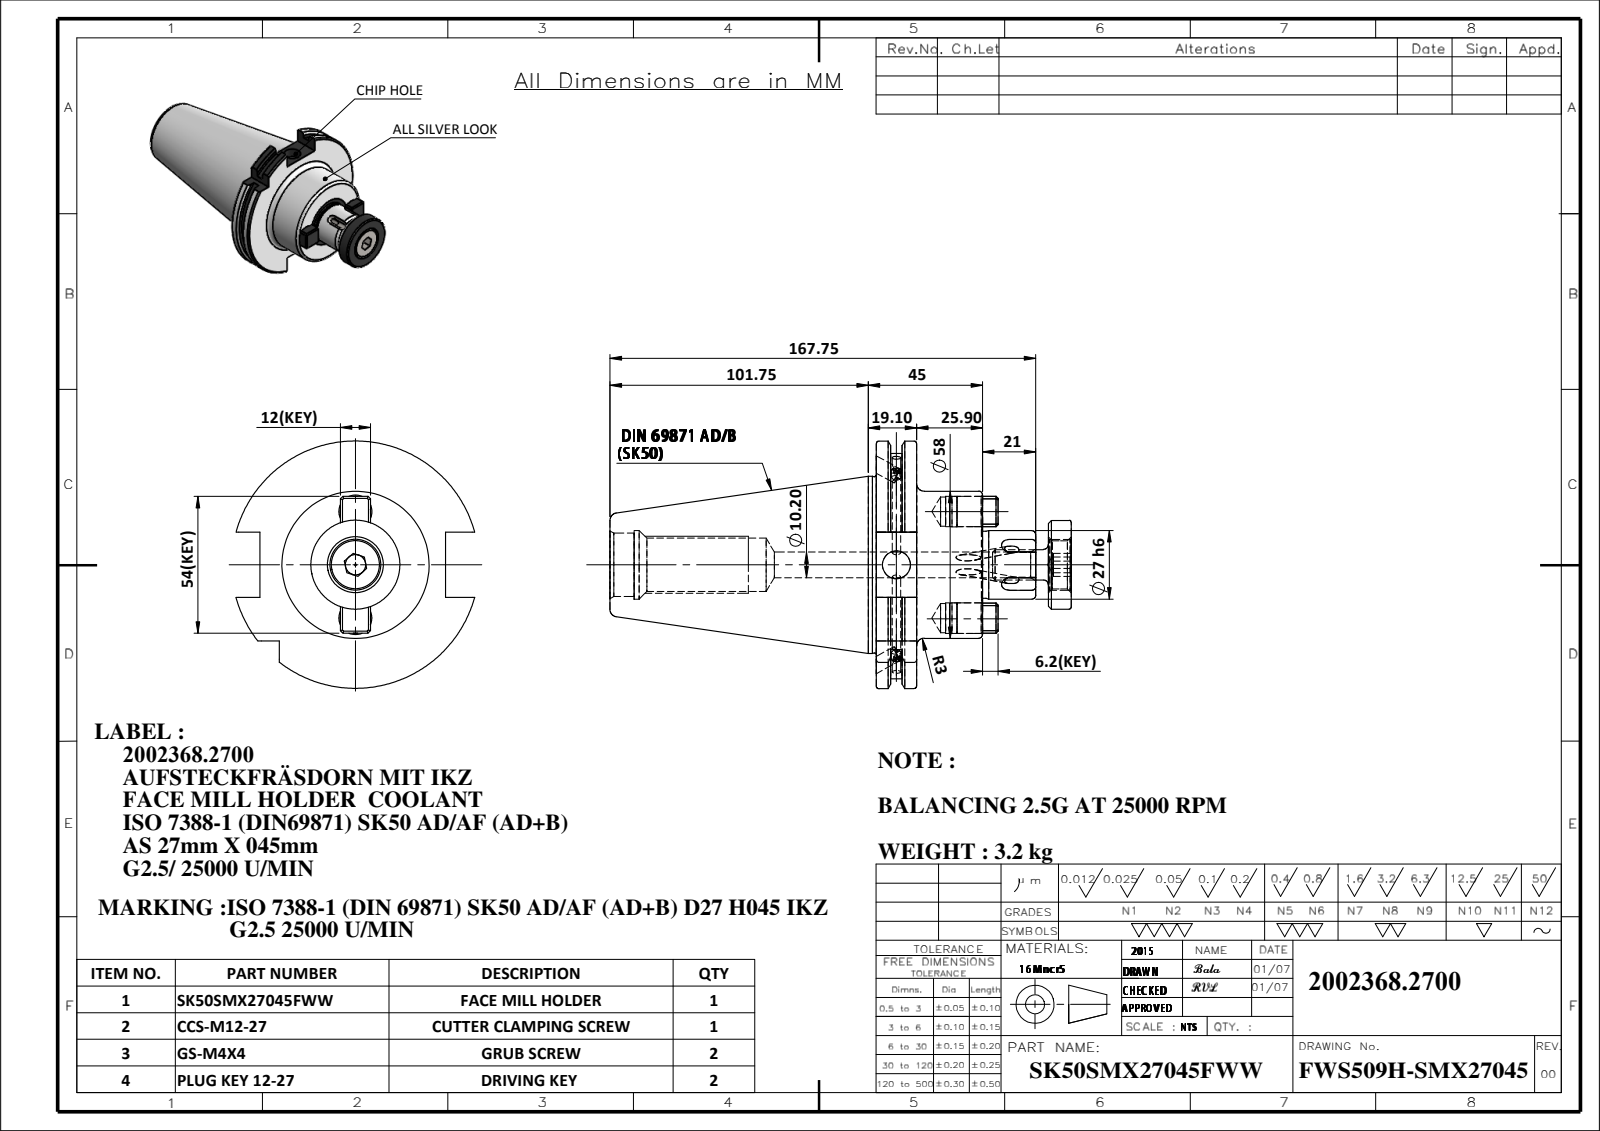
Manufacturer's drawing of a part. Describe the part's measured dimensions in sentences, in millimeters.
The part is named "CCS-M12-27; CCS-M12-27-2; 91506-AS327045; M4X4_DIN 913 - M4 x 4-N (+3 more)". Its 3-D file was written by "SolidWorks 2018 (CONFIG_CONTROL_DESIGN)". It is 7 solids with 318 faces: 108 planar, 93 cylindrical and 117 other. Overall it measures 181.75 by 97.5 by 94.05 millimeters. Its volume is 420 010 cubic millimeters and its surface area 59 907 square millimeters. Round holes: 4 of diameter 3, 2 of diameter 6, 2 of diameter 11.5, 2 of diameter 12, 1 of diameter 3.3, 1 of diameter 10.2, 1 of diameter 11, 1 of diameter 19, 1 of diameter 21, 1 of diameter 25, 1 of diameter 27. Round bosses or shafts: 2 of diameter 12.02, 2 of diameter 12.02, 2 of diameter 4, 1 of diameter 69.85, 1 of diameter 69.45, 1 of diameter 58, 1 of diameter 35, 1 of diameter 26.4. Partial cylindrical surfaces (rounded edges, fillets, slot ends): 4 of radius 2, 2 of radius 7.75, 1 of radius 44.9, 1 of radius 48.75. The main face-to-face distances are 15.9, 41.8, 25.9, 76.8, 60.9, 35, 5.66, 10.24, 36.14, 71.14. The hole center spacings are 21, 42.
